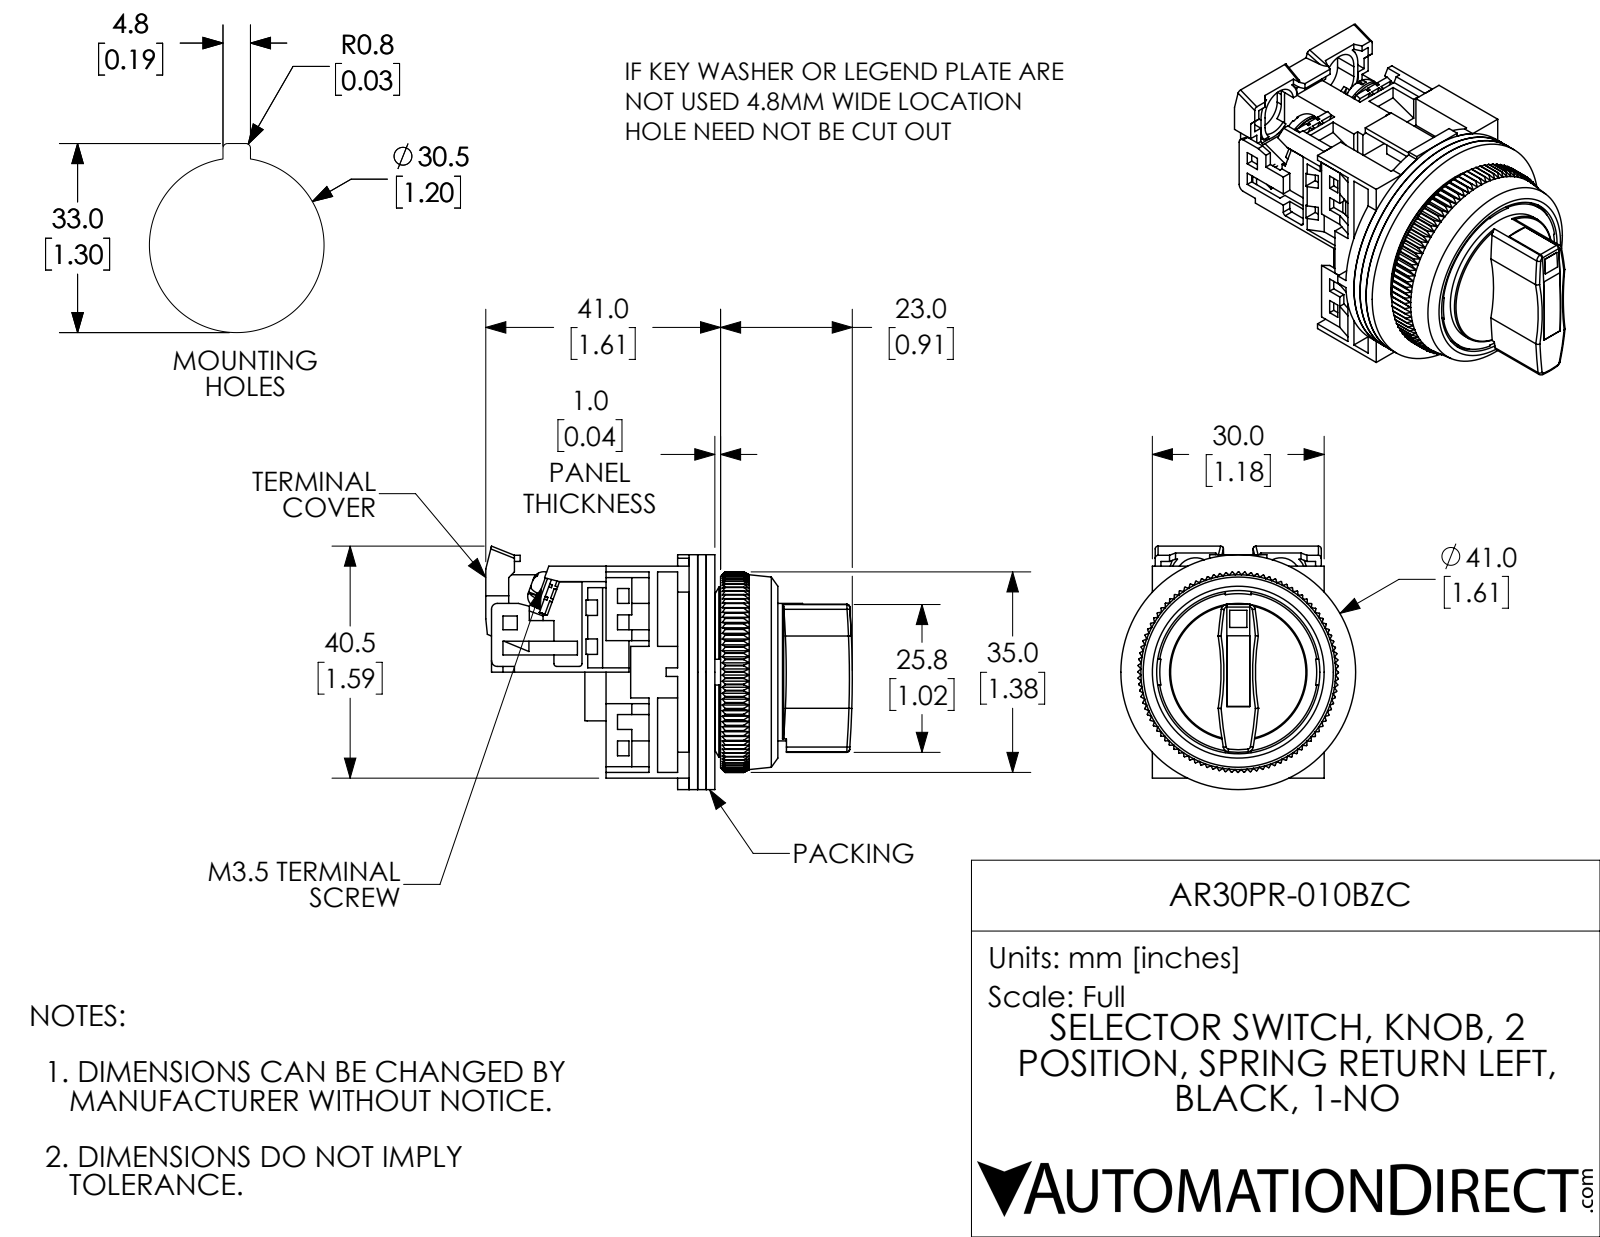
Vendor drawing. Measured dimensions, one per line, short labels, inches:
name: AR30PR-010BZC
written by: SolidWorks 2017 (AUTOMOTIVE_DESIGN)
unit: in
bodies: 18 solids, 1327 faces (832 planar, 283 cylindrical, 212 other)
size: 2.52 × 1.673 × 1.614
volume: 1.842 in³; area: 53.12 in²
holes: 4× ⌀0.138, 2× ⌀0.142, 1× ⌀0.118, 1× ⌀0.315, 1× ⌀0.472, 1× ⌀0.48, 1× ⌀0.512, 1× ⌀0.819, 1× ⌀0.945, 1× ⌀1.122, 1× ⌀1.252
bosses: 2× ⌀0.26, 2× ⌀0.138, 1× ⌀1.614, 1× ⌀1.181, 1× ⌀0.787, 1× ⌀0.709, 1× ⌀0.669, 1× ⌀0.559
rounds: 8× R0.059, 7× R0.02, 6× R0.039, 2× R0.138, 2× R0.177, 2× R1.575, 2× R1.638, 2× R2.89
face distances: 0.059, 0.118, 0.177, 0.039, 0.197, 0.079, 0.157, 0.512, 0.689, 0.138
hole spacings: 0.579, 0.61
